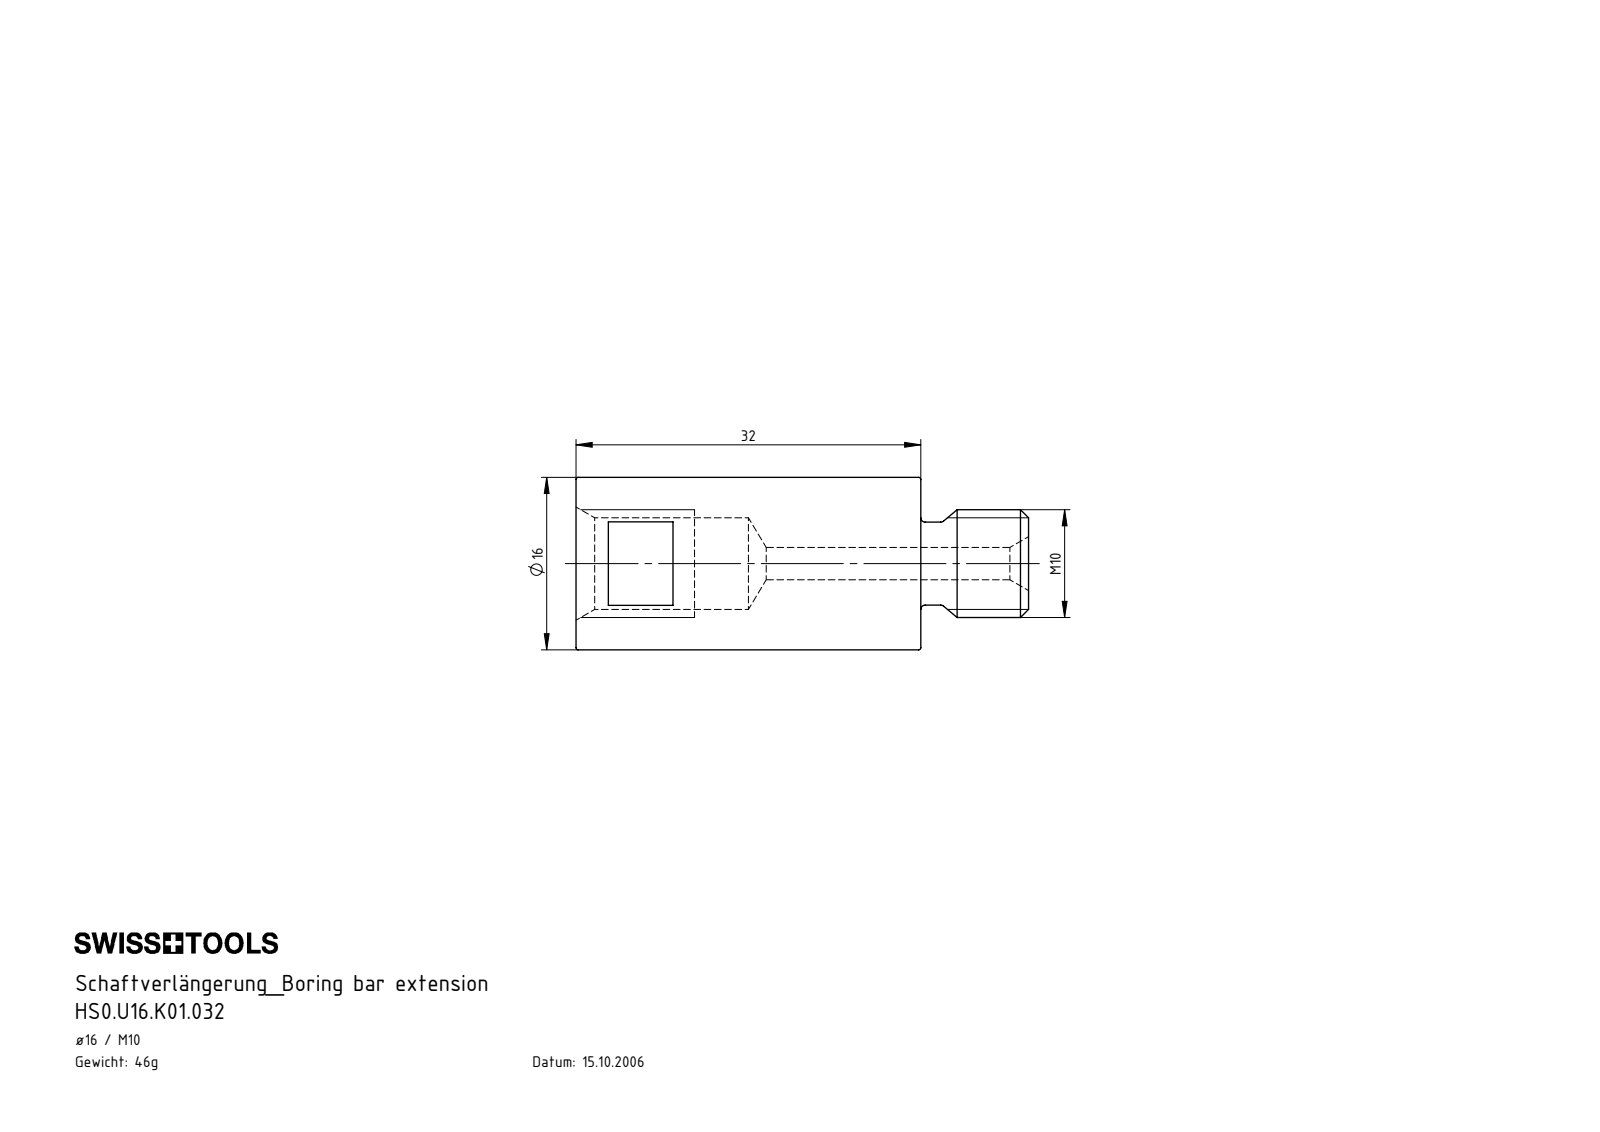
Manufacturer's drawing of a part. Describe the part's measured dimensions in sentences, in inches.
The part is named "HS0.U16.K01.032". Its 3-D file was written by "SolidWorks 2017 (AUTOMOTIVE_DESIGN)". It is 1 solid with 23 faces: 9 planar, 5 cylindrical and 9 other. Overall it measures 1.654 by 0.63 by 0.63 inches. Its volume is 0.36 cubic inches and its surface area 4.602 square inches. Round holes: 1 of diameter 0.118, 1 of diameter 0.335. Round bosses or shafts: 1 of diameter 0.63, 1 of diameter 0.394, 1 of diameter 0.303. The main face-to-face distances are 1.26, 0.551, 0.394, 1.654, 1.535, 1.142, 0.118, 1.299, 0.906, 0.236.
